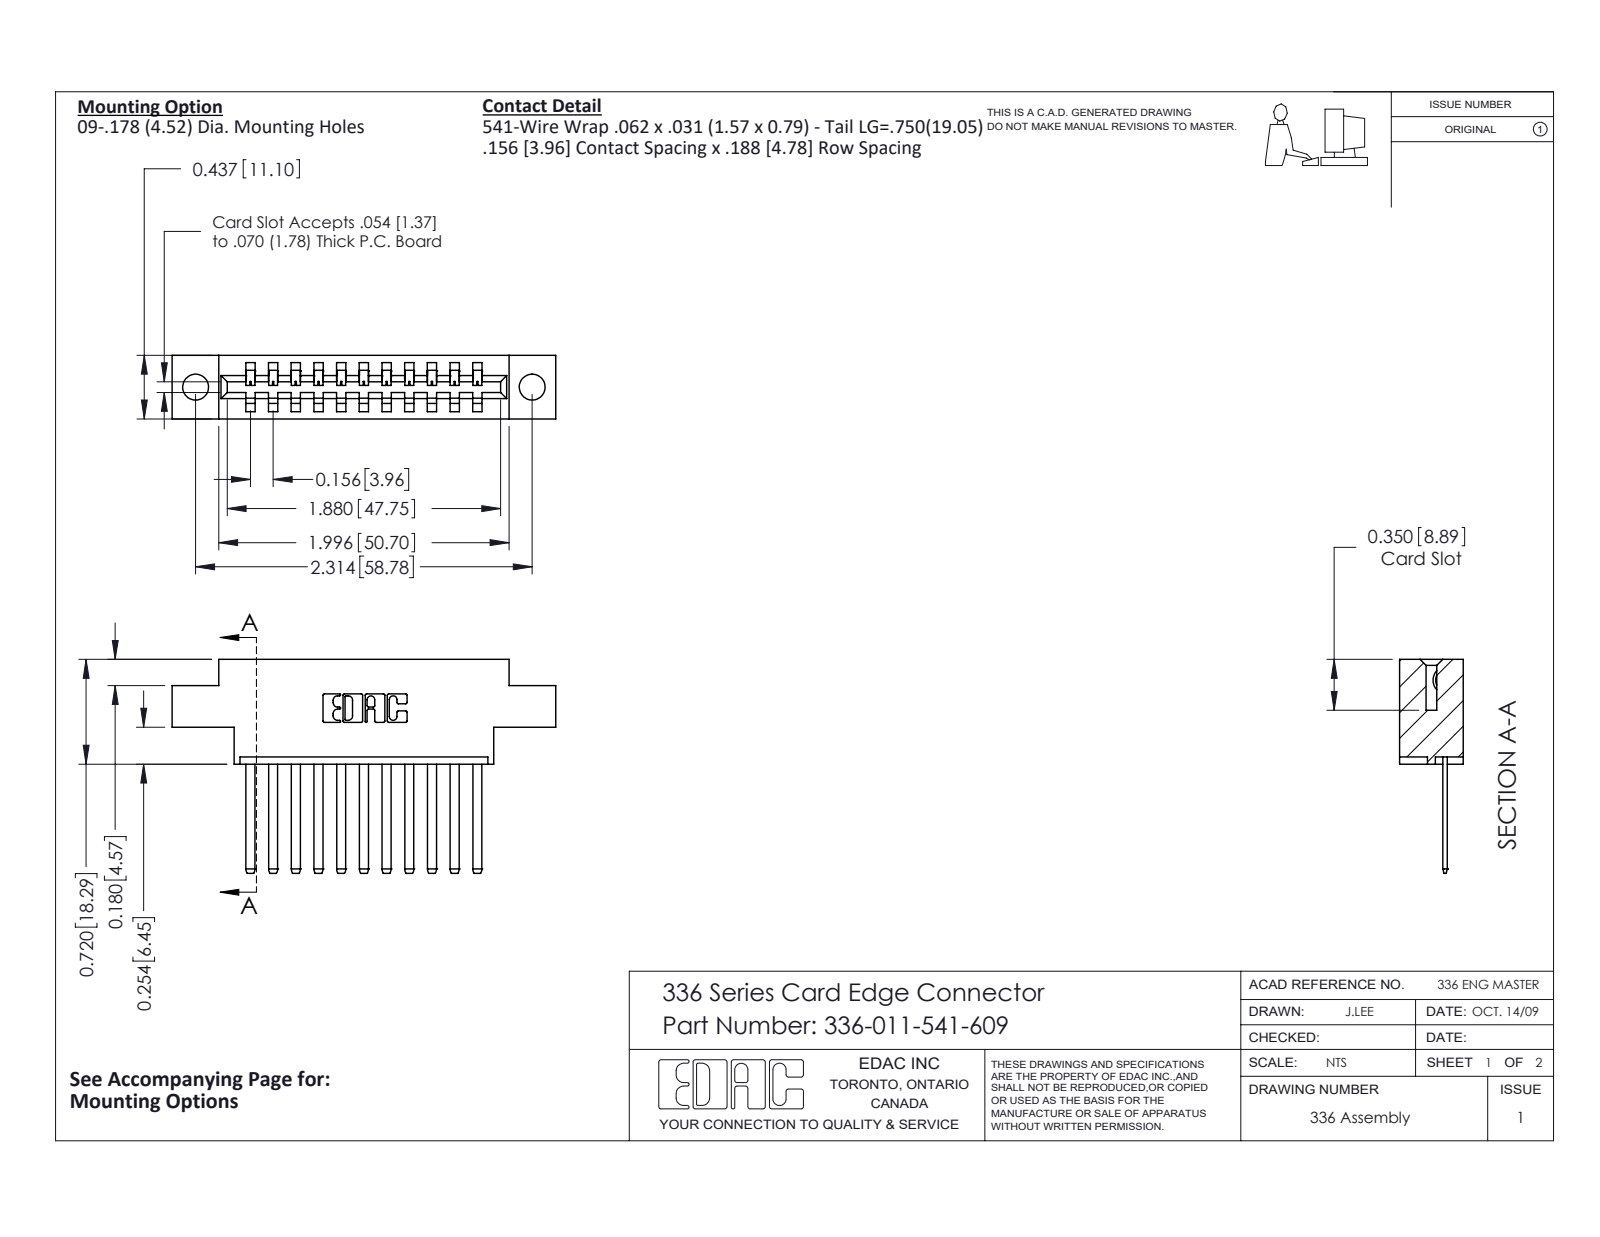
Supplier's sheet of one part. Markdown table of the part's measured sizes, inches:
| quantity | value |
| --- | --- |
| part name | 336-011-541-609; 336 Part_Offset - .178 Dia - TH; 336-290-001_336-290-541 |
| STEP written by | SolidWorks 2020 (CONFIG_CONTROL_DESIGN) |
| units | inches |
| bodies | 12 solids, 668 faces (448 planar, 220 cylindrical, 0 other) |
| overall size | 2.637 × 1.47 × 0.437 |
| volume | 0.532 in³ |
| surface area | 14.02 in² |
| round holes (diameter × count) | 0.178 × 2 |
| partial cylindrical surfaces (radius × count) | 0.004 × 22, 0.01 × 22, 0.056 × 22, 0.007 × 6, 0.031 × 6, 0.026 × 3, 0.022 × 2, 0.04 × 2 |
| main face-to-face distances | 0.437, 0.156, 0.468, 0.624, 0.312, 0.78, 0.181, 0.256, 0.312, 0.404 |
| hole center spacings | 2.314 |
